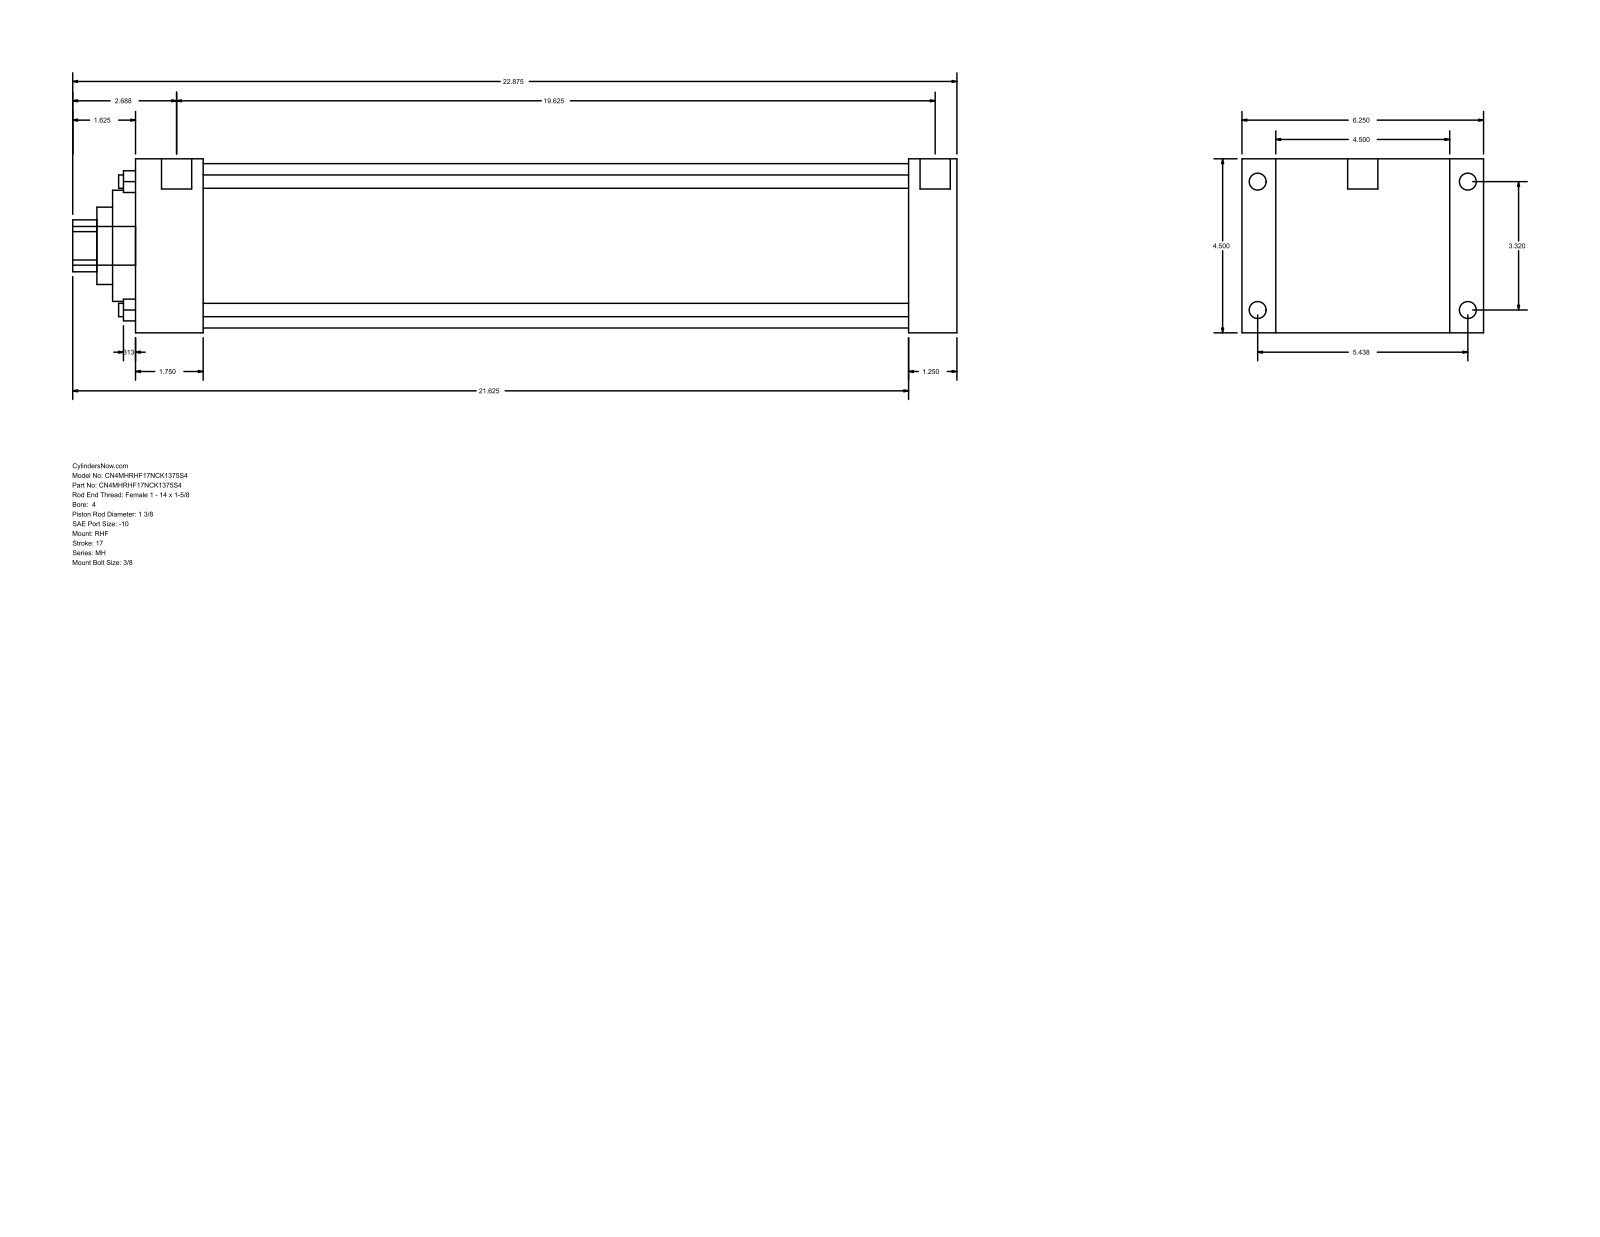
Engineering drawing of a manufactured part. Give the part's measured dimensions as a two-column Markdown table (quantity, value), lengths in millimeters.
| quantity | value |
| --- | --- |
| part name | MH_RHF__0400_1.375 |
| STEP written by | GSSL Pune (CONFIG_CONTROL_DESIGN) |
| units | millimeters |
| bodies | 0 solids, 90 faces (61 planar, 29 cylindrical, 0 other) |
| overall size | 581.02 × 158.75 × 114.3 |
| round holes (diameter × count) | 8.76 × 4, 34.92 × 1, 50.8 × 1, 73.03 × 1, 107.95 × 1 |
| round bosses / shafts (diameter × count) | 11.13 × 4, 8.73 × 4, 19.84 × 2, 25.4 × 1 |
| partial cylindrical surfaces (radius × count) | 17.06 × 1 |
| main face-to-face distances | 114.3, 539.75, 508, 31.75, 22.23, 136.53, 44.45, 463.55, 495.3, 158.76 |
| hole center spacings | 59.62, 84.32, 119.25 |
